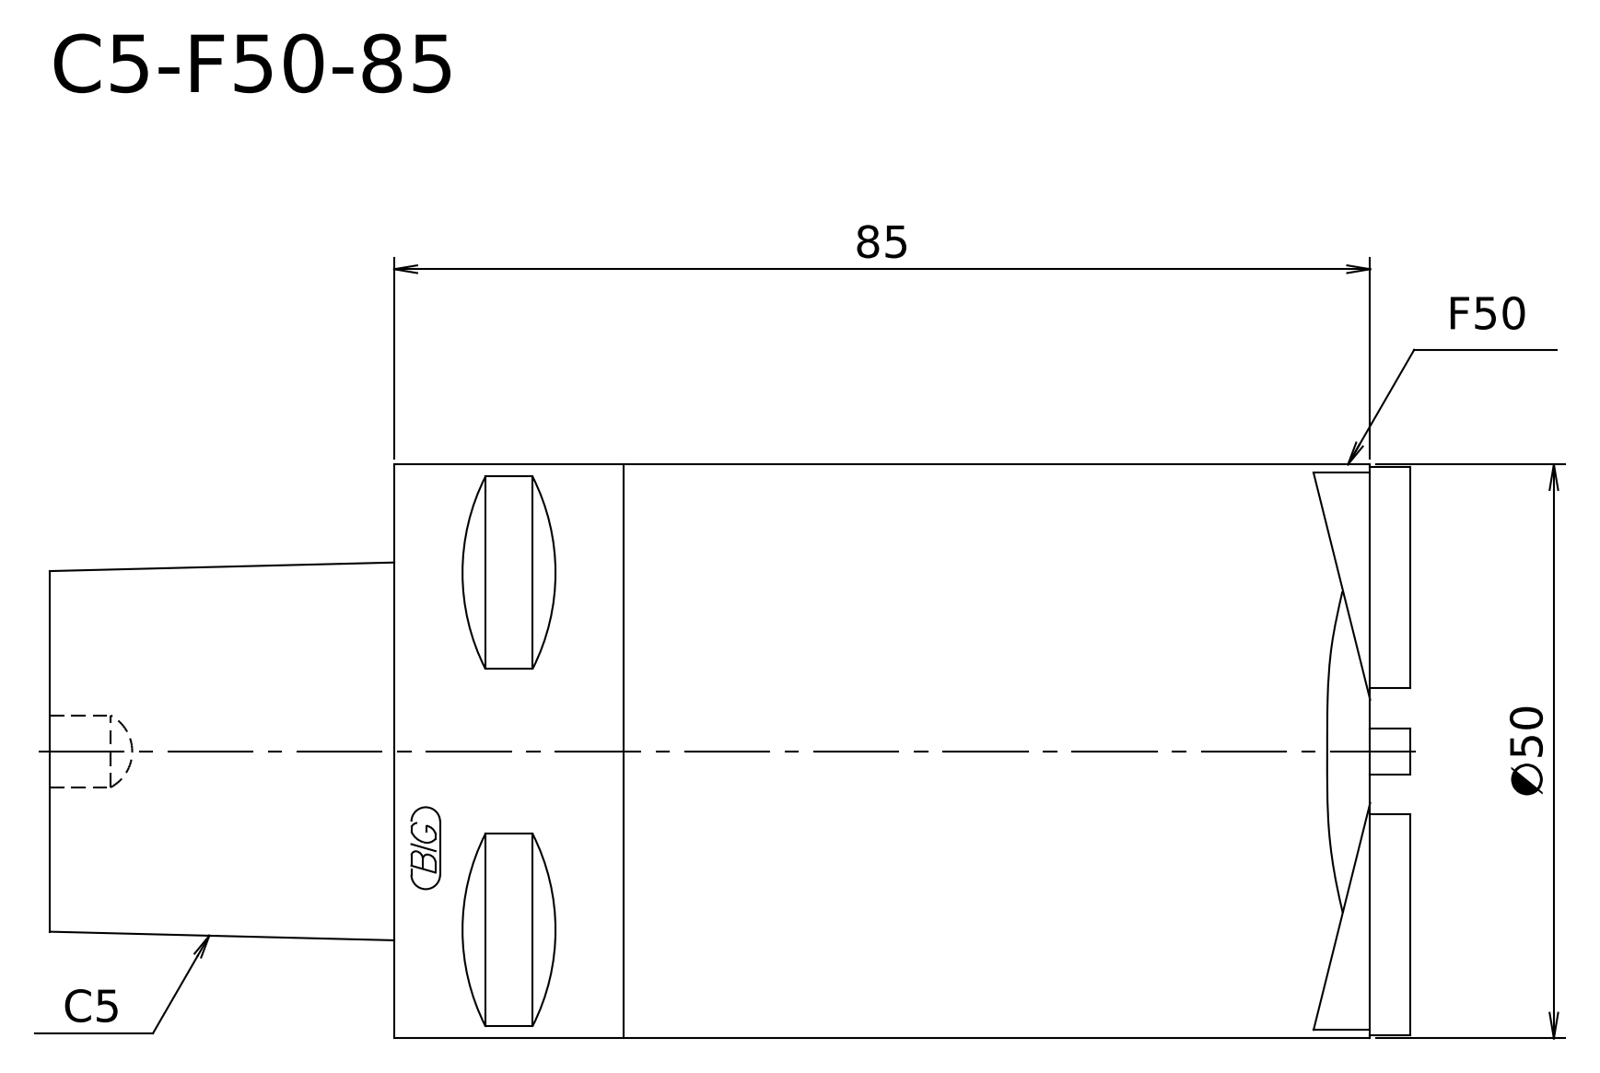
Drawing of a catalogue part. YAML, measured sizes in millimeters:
part_name: "C5-F50-85"
step_written_by: "SolidWorks 2021 (CONFIG_CONTROL_DESIGN)"
units: millimeters
bodies: {solids: 1, faces: 7, planar: 3, cylindrical: 2, other: 2}
overall_size: [115, 50, 50]
volume: 191271
surface_area: 20235
round_bosses_or_shafts:
  - {diameter: 50, count: 1}
face_to_face_distances: [85, 30, 115]
